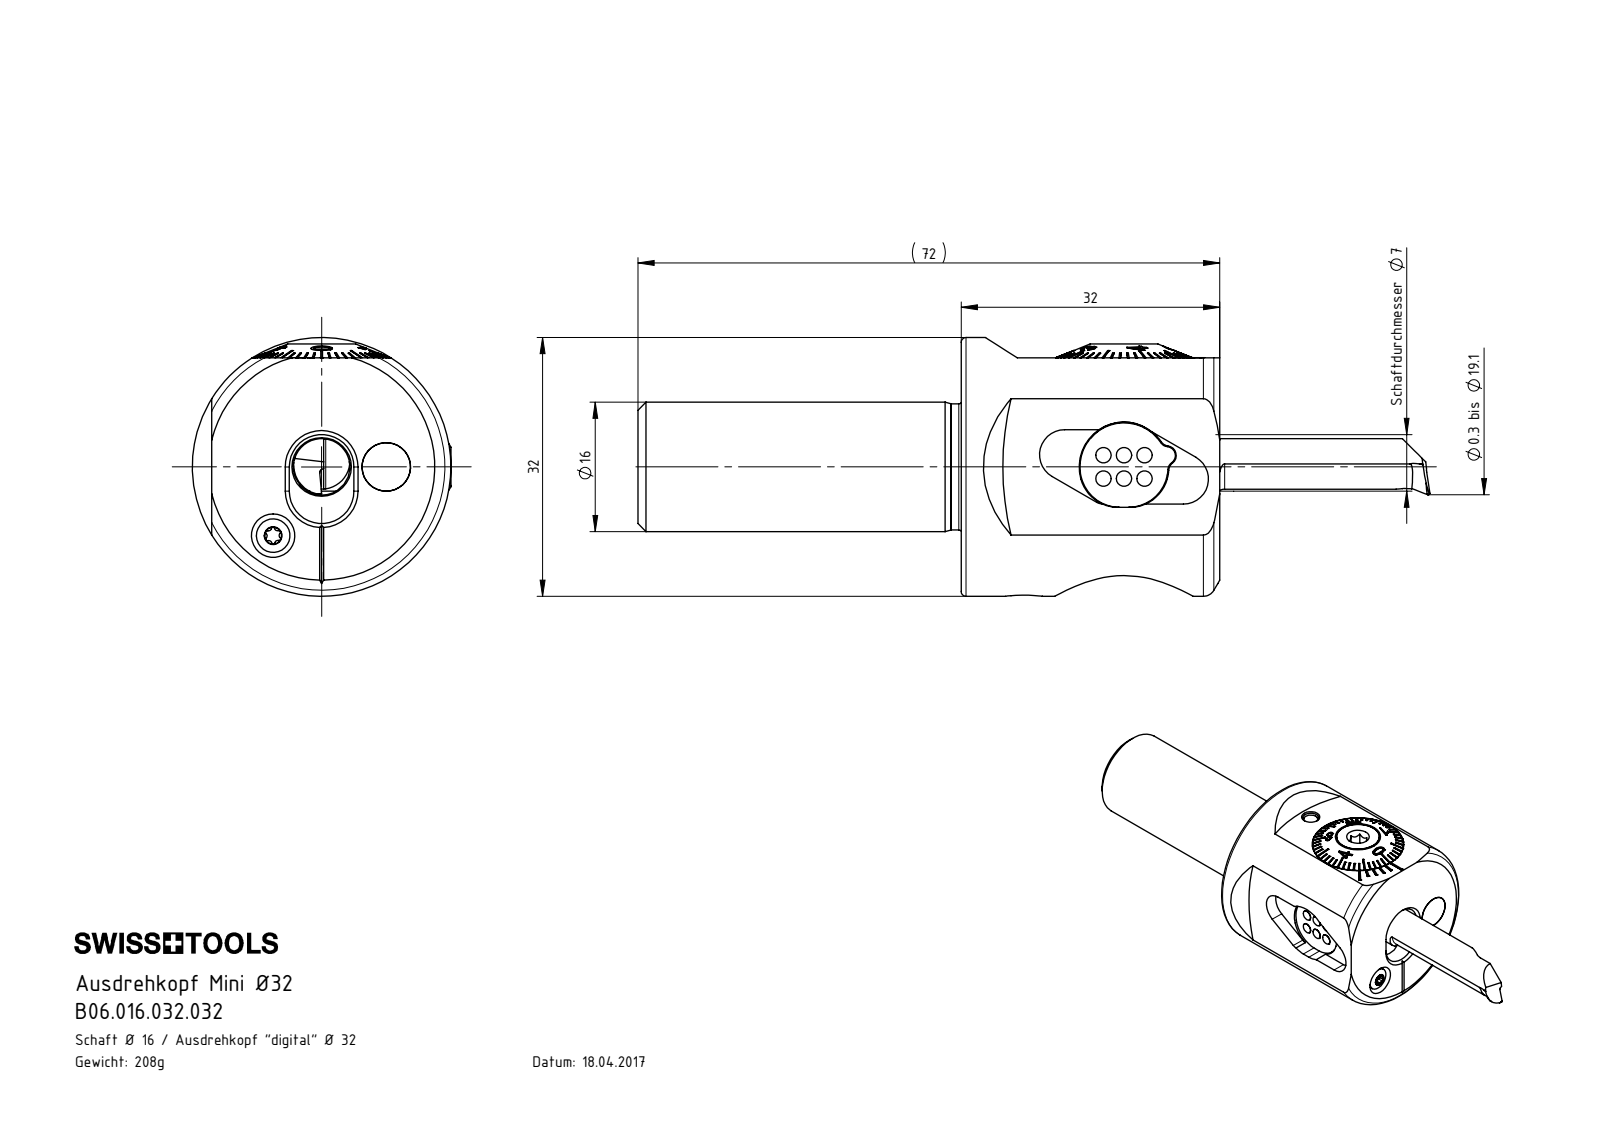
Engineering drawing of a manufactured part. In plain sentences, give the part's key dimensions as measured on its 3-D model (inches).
The part is named "F32-BG2.017.004_A; A32-BG2.009.004_A; Klebstoff D6; DIN 3771 - 15x1 (+8 more)". Its 3-D file was written by "SolidWorks 2017 (CONFIG_CONTROL_DESIGN)". It is 18 solids with 822 faces: 360 planar, 180 cylindrical and 282 other. Overall it measures 3.858 by 1.26 by 1.26 inches. Its volume is 1.743 cubic inches and its surface area 27.75 square inches. Round holes: 7 of diameter 0.197, 2 of diameter 0.13, 1 of diameter 0.028, 1 of diameter 0.039, 1 of diameter 0.079, 1 of diameter 0.098, 1 of diameter 0.114, 1 of diameter 0.118, 1 of diameter 0.236, 1 of diameter 0.276, 1 of diameter 0.305, 1 of diameter 0.331. Round bosses or shafts: 6 of diameter 0.075, 3 of diameter 0.236, 1 of diameter 1.26, 1 of diameter 0.669, 1 of diameter 0.669, 1 of diameter 0.663, 1 of diameter 0.63, 1 of diameter 0.614. Partial cylindrical surfaces (rounded edges, fillets, slot ends): 6 of radius 0.008, 5 of radius 0.014, 4 of radius 0.008, 4 of radius 0.087, 3 of radius 0.043, 3 of radius 0.047, 2 of radius 0.122, 2 of radius 0.157. The main face-to-face distances are 1.26, 0.177, 0.059, 0.031, 0.016, 0.161, 0.102, 0.268, 0.091, 0.193. The hole center spacings are 0.177, 0.274, 0.512, 0.103, 0.112, 0.311, 0.315, 0.354.
